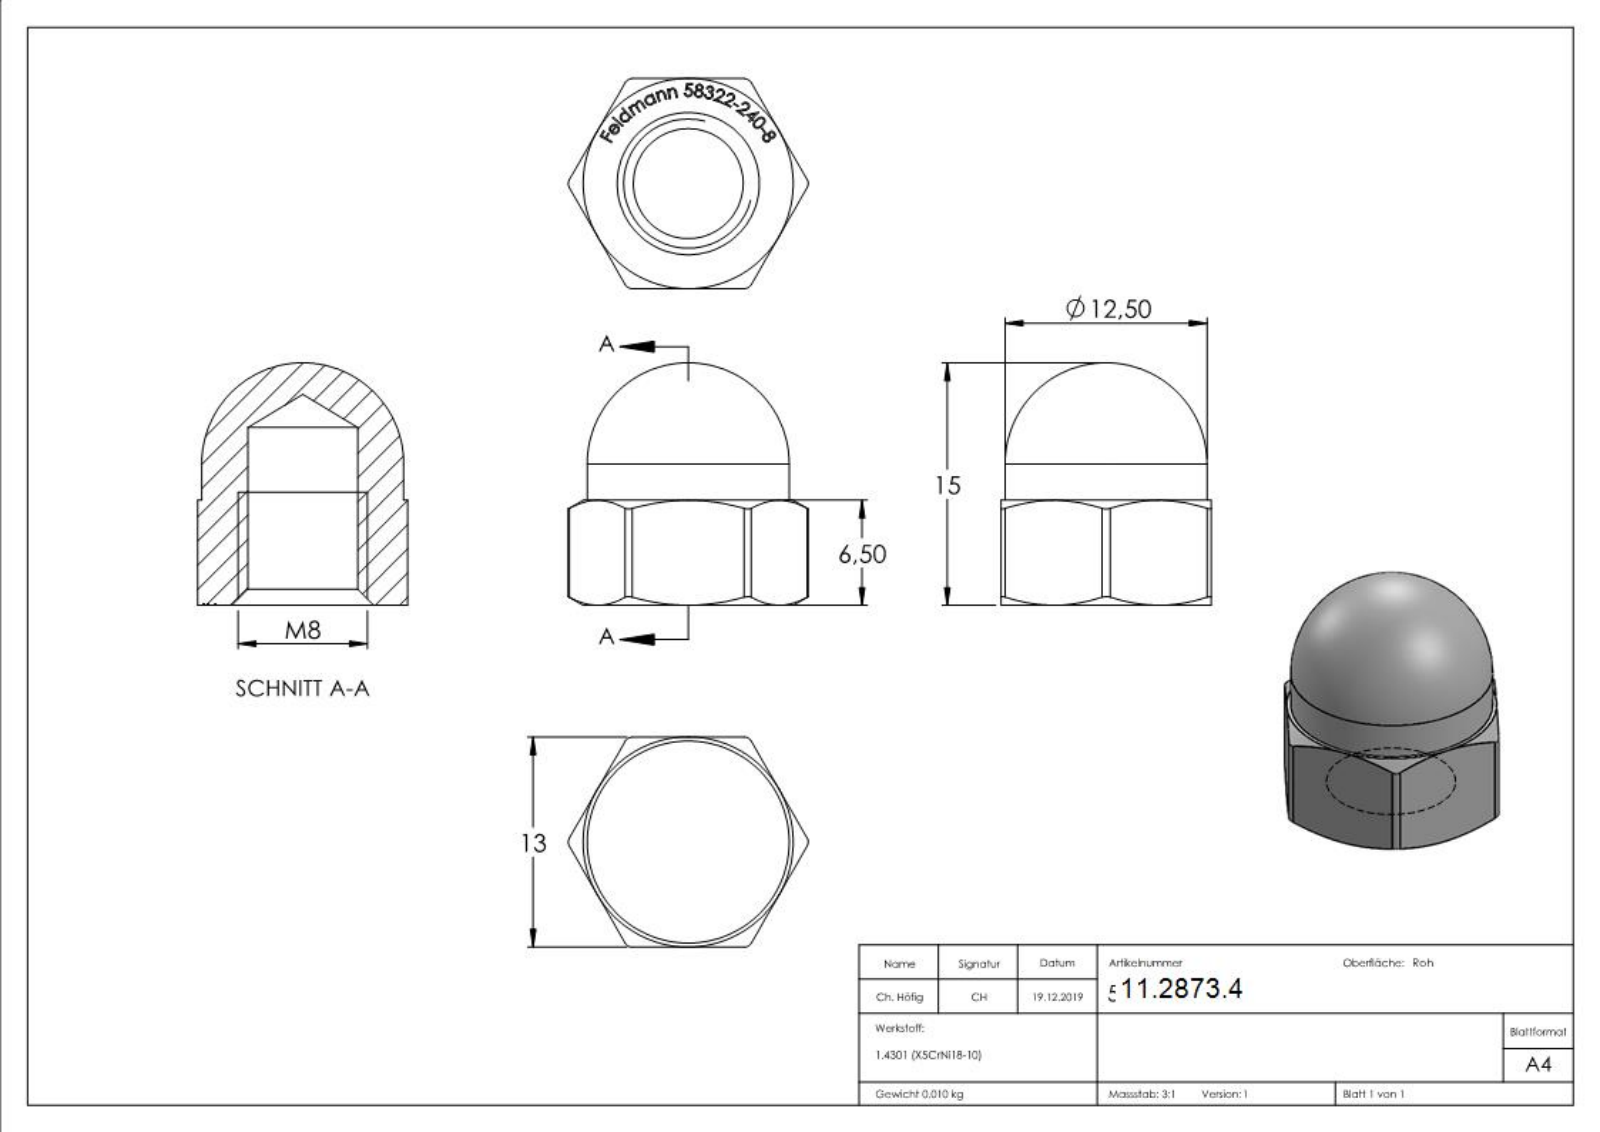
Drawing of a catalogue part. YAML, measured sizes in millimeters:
part_name: "58322-240-8"
step_written_by: "SolidWorks 2015 (CONFIG_CONTROL_DESIGN)"
units: millimeters
bodies: {solids: 1, faces: 292, planar: 138, cylindrical: 8, other: 146}
overall_size: [20, 14.86, 13]
volume: 1297
surface_area: 1017
round_holes:
  - {diameter: 6.8, count: 1}
round_bosses_or_shafts:
  - {diameter: 12.5, count: 1}
partial_cylinders:
  - {radius: 0.5, count: 6}
face_to_face_distances: [13, 6.5, 6.4, 0.4, 0.32, 0.43, 0.8, 0.48, 0.36, 0.88]
